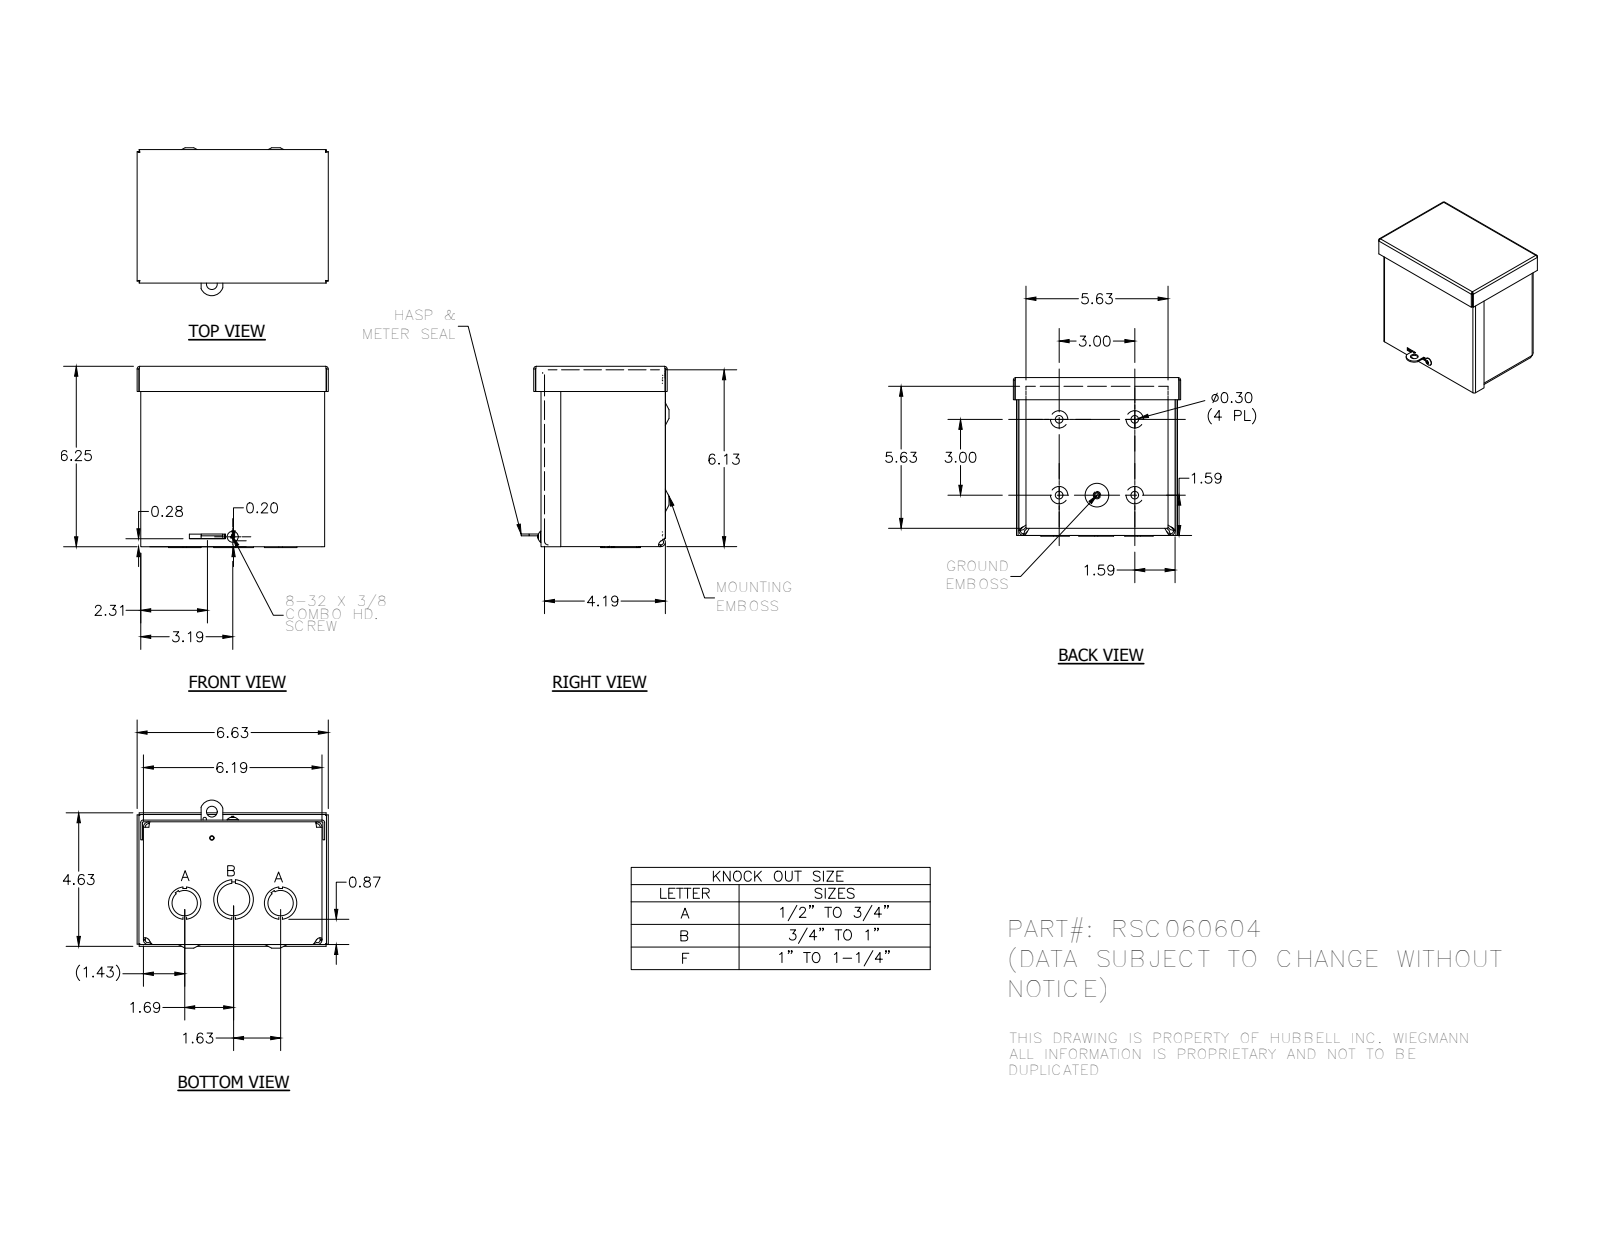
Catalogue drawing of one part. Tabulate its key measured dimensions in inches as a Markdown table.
| quantity | value |
| --- | --- |
| part name | RSC060604; RSC060604_WRAP; RSC0606_LID; RSC0604_CAP (+4 more) |
| STEP written by | Autodesk Inventor 2012 (AUTOMOTIVE_DESIGN) |
| units | inches |
| bodies | 6 solids, 461 faces (220 planar, 116 cylindrical, 125 other) |
| overall size | 6.625 × 6.281 × 5.125 |
| volume | 16.05 in³ |
| surface area | 529.5 in² |
| round holes (diameter × count) | 0.3 × 4, 1.125 × 3, 0.125 × 2, 0.313 × 2, 0.875 × 2, 0.148 × 1, 0.156 × 1, 0.165 × 1, 0.375 × 1, 1.375 × 1 |
| round bosses / shafts (diameter × count) | 0.384 × 1, 0.229 × 1, 0.164 × 1 |
| partial cylindrical surfaces (radius × count) | 0.01 × 10, 0.031 × 8, 0.093 × 8, 0.125 × 8, 0.187 × 8, 0.021 × 4, 0.031 × 4, 0.055 × 4 |
| main face-to-face distances | 0.062, 6.126, 0.062, 4.249, 6.188, 0.124, 4.187, 0.063, 4.312, 4.25 |
| hole center spacings | 3, 1.5, 3.354, 4.243, 0.358, 0.702, 0.913, 1.252 |
